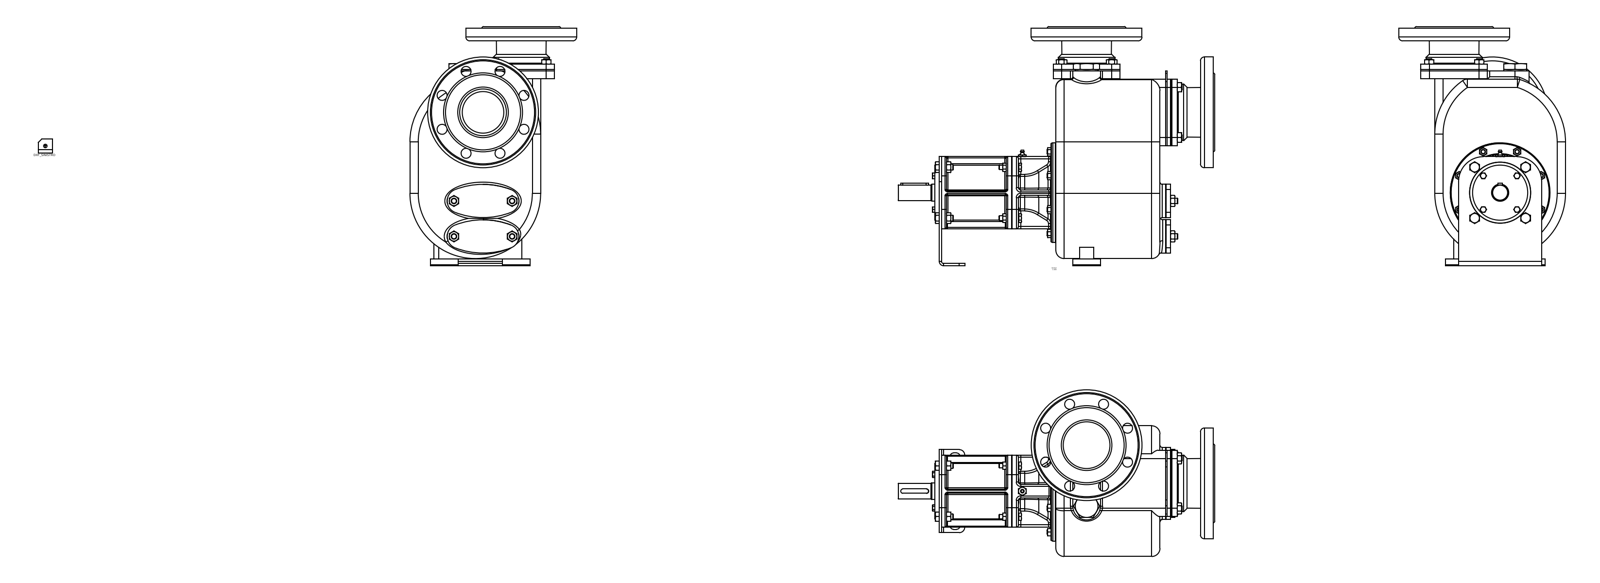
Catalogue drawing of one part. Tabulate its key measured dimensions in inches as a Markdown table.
| quantity | value |
| --- | --- |
| part name | S_82_K_B_F |
| STEP written by | CREO PARAMETRIC BY PTC INC, 2017110 (CONFIG_CONTROL_DESIGN) |
| units | inches |
| bodies | 1 solid, 1003 faces (233 planar, 406 cylindrical, 364 other) |
| overall size | 22.5 × 17.008 × 11.85 |
| volume | 987.4 in³ |
| surface area | 1 475 in² |
| round holes (diameter × count) | 0.709 × 16, 0.433 × 14, 0.394 × 12, 0.453 × 12, 0.276 × 4, 0.787 × 4, 0.335 × 2, 3.319 × 2, 3.327 × 2, 3.543 × 2, 4.843 × 2, 5.335 × 2 |
| round bosses / shafts (diameter × count) | 7.874 × 2, 5.61 × 2, 5.236 × 2, 4.528 × 2, 4.016 × 2, 1.969 × 2, 7.087 × 1, 5.512 × 1 |
| partial cylindrical surfaces (radius × count) | 0.157 × 38, 0.079 × 22, 0.118 × 22, 0.591 × 19, 5.512 × 8, 0.256 × 4, 0.866 × 4, 0.866 × 4 |
| main face-to-face distances | 7.402, 0.827, 2.874, 2.323, 2.677, 0.315, 0.197, 0.236, 0.472, 1.024 |
| hole center spacings | 3.15, 4.454, 1.267, 3.193, 4.727, 5.561, 2.41, 2.411 |
